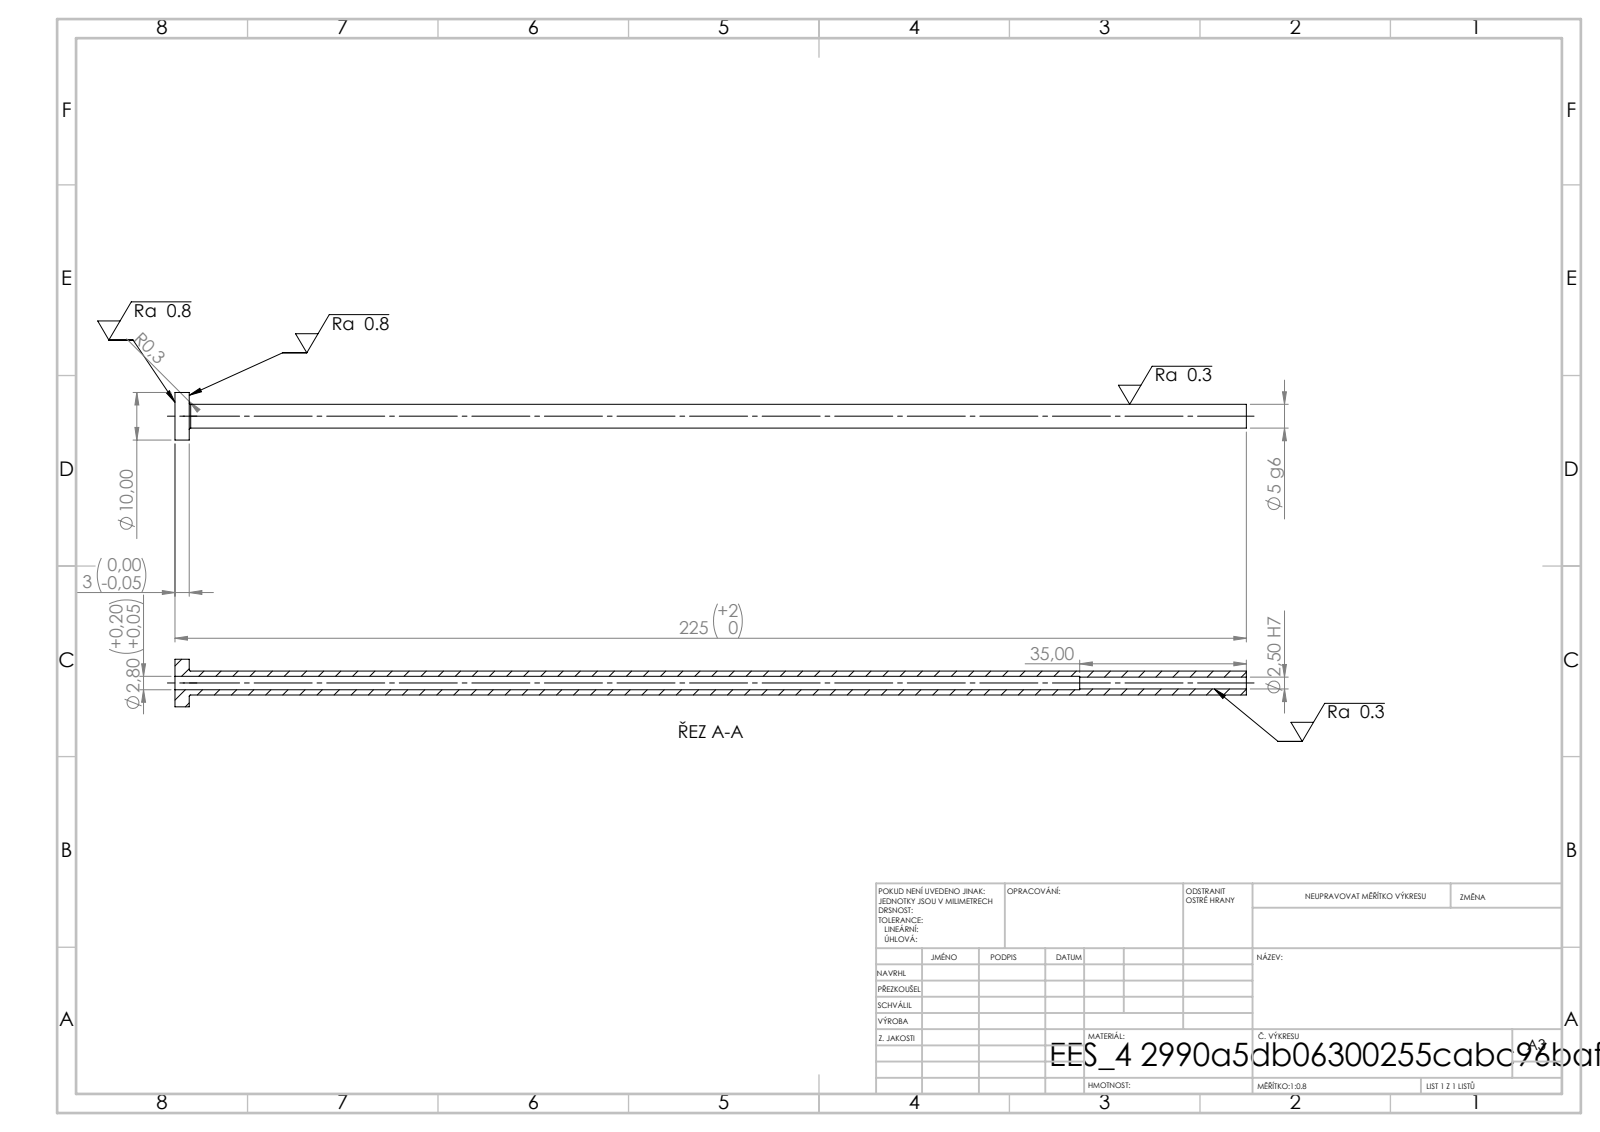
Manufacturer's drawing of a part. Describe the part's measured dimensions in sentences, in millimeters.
Its 3-D file was written by "SolidWorks 2019 (CONFIG_CONTROL_DESIGN)". It is 1 solid with 14 faces: 4 planar, 8 cylindrical and 2 other. Overall it measures 225 by 10 by 10 millimeters. Its volume is 3 253 cubic millimeters and its surface area 5 673 square millimeters. Round holes: 1 of diameter 2.5, 1 of diameter 2.8. Round bosses or shafts: 1 of diameter 10, 1 of diameter 5. The main face-to-face distances are 3, 225, 222, 190, 187, 35.
